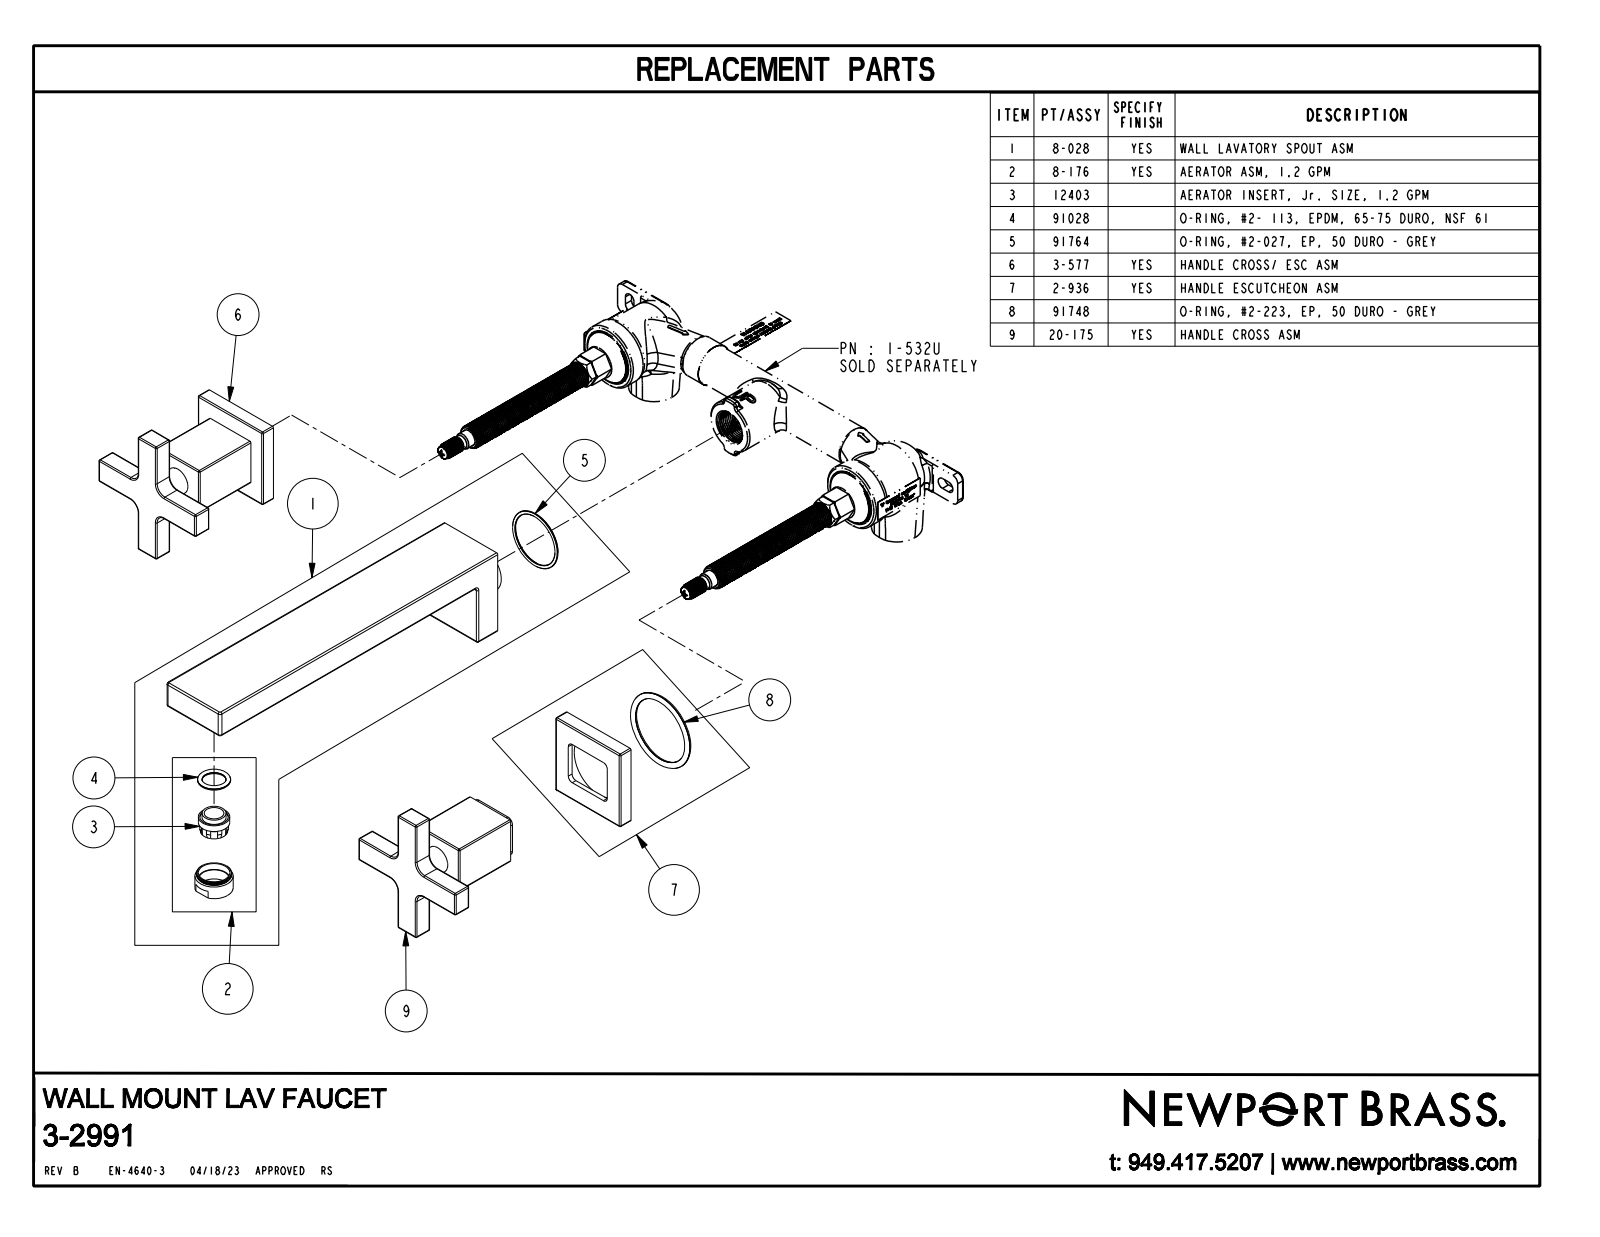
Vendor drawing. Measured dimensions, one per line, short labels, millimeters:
name: 3-2991_SW0001
written by: CREO PARAMETRIC BY PTC INC, 2018400 (AUTOMOTIVE_DESIGN)
unit: mm
bodies: 3 solids, 275 faces (67 planar, 132 cylindrical, 76 other)
size: 279.8 × 239.7 × 79.8
volume: 398 700 mm³; area: 76 770 mm²
bosses: 2× ⌀16.5, 2× ⌀13.3, 1× ⌀41.9, 1× ⌀27.9, 1× ⌀22.2
rounds: 68× R0.8, 11× R1, 8× R6.4, 2× R1.5, 1× R2
face distances: 16.6, 200, 26.1, 77.4, 44.5, 13.2, 60.8, 65.9, 11.4, 42.7
